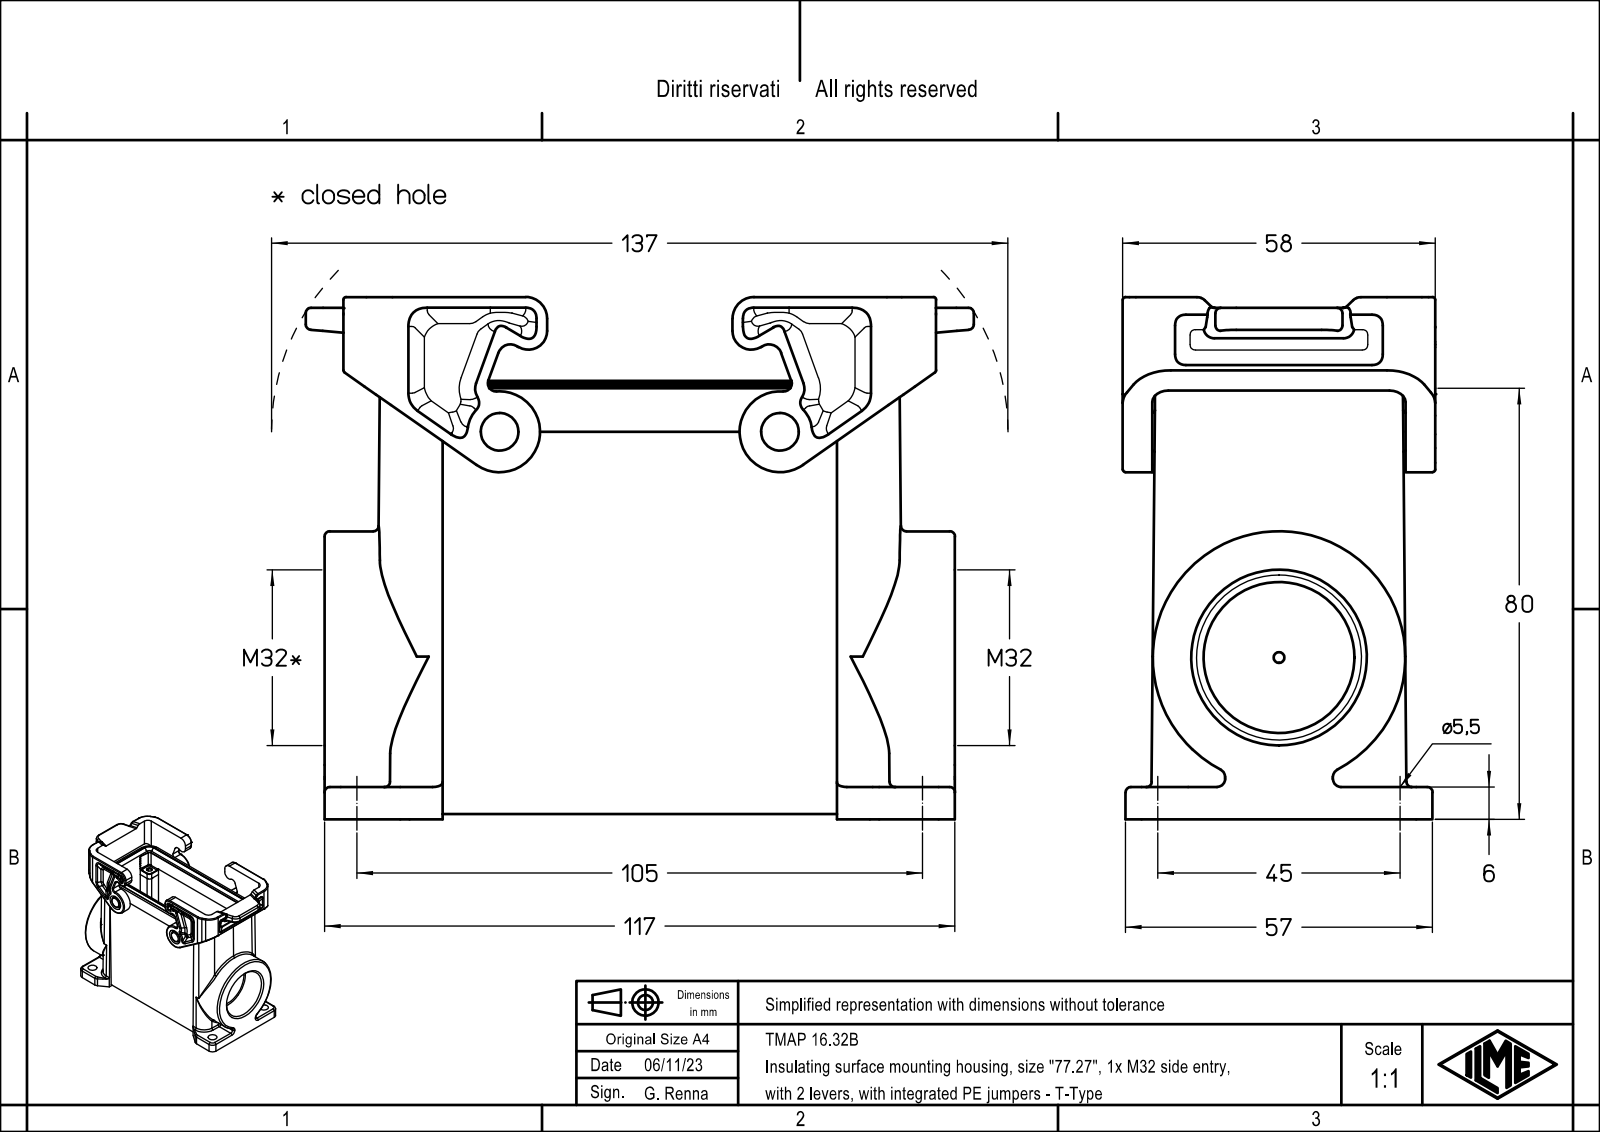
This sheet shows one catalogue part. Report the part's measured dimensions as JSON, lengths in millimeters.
{"part_name": "TMAP 16.32B", "step_written_by": "Creo Elements/Direct Modeling 20.1B 02-Apr-2019 (C) Parametric Technology GmbH (AUTOMOTIVE_DESIGN)", "units": "millimeters", "bodies": {"solids": 1, "faces": 610, "planar": 364, "cylindrical": 194, "other": 52}, "overall_size": [124, 96.9, 58], "volume_mm3": 198944, "surface_area_mm2": 73592, "round_holes": [[3.5, 4], [5.5, 4], [28, 1], [30.6, 1]], "round_bosses_or_shafts": [[7, 2], [46.87, 1]], "partial_cylinders_radius": [[2, 20], [3, 20], [1.5, 18], [1, 16], [1.3, 12], [6, 8], [7, 8], [4, 6]], "face_to_face_distances": [35.2, 5.5, 5.9, 41.1, 6.5, 1, 11.4, 46.6, 52.5, 11.8], "hole_center_spacings": [16.43, 38.54, 91.69, 98.09, 27, 45, 77.5, 82.07]}
